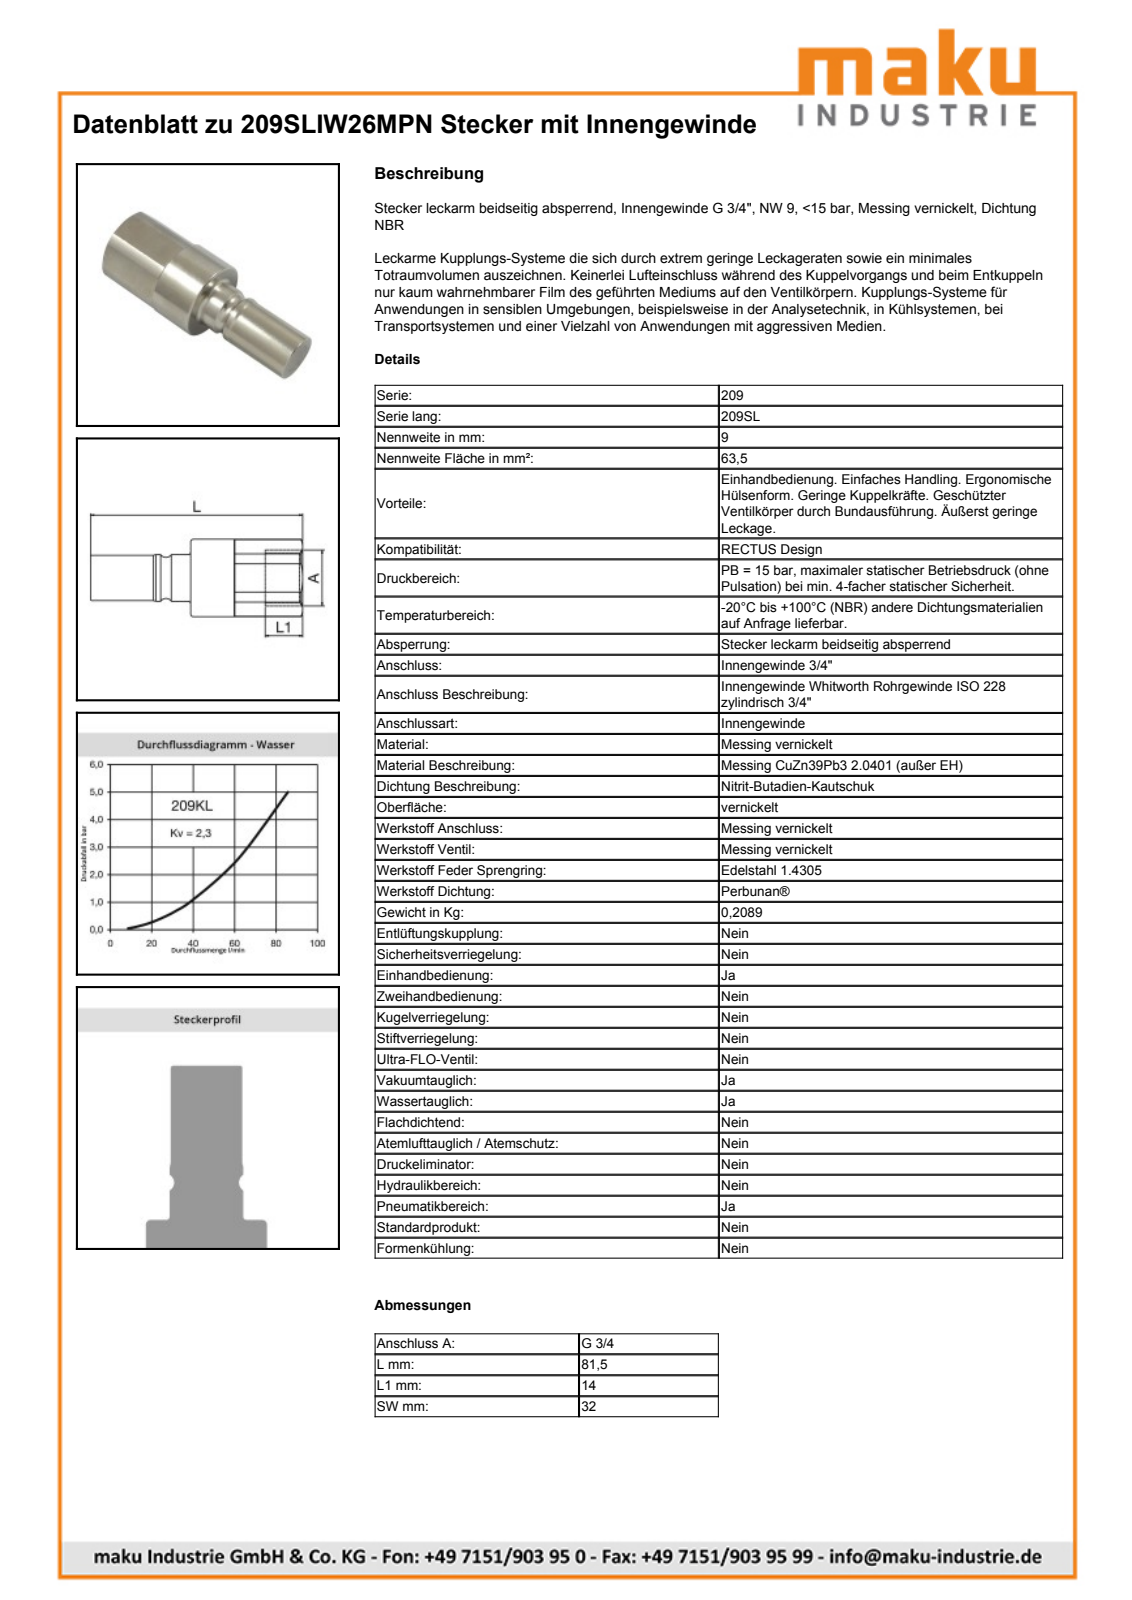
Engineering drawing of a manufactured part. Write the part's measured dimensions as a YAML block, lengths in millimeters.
part_name: "D110819"
step_written_by: "Autodesk Inventor 2013 (AUTOMOTIVE_DESIGN)"
units: millimeters
bodies: {solids: 1, faces: 59, planar: 14, cylindrical: 17, other: 28}
overall_size: [81.4, 36.1, 32.29]
volume: 36020
surface_area: 10177
round_holes:
  - {diameter: 18.6, count: 1}
  - {diameter: 24.12, count: 1}
  - {diameter: 25, count: 1}
  - {diameter: 26.8, count: 1}
round_bosses_or_shafts:
  - {diameter: 29, count: 1}
  - {diameter: 24.61, count: 1}
  - {diameter: 17.47, count: 1}
  - {diameter: 16.97, count: 1}
partial_cylinders:
  - {radius: 18.05, count: 1}
face_to_face_distances: [32, 32.02, 27.89, 43.9, 16.01, 37.5, 65.39, 81.4, 54, 16.5]
